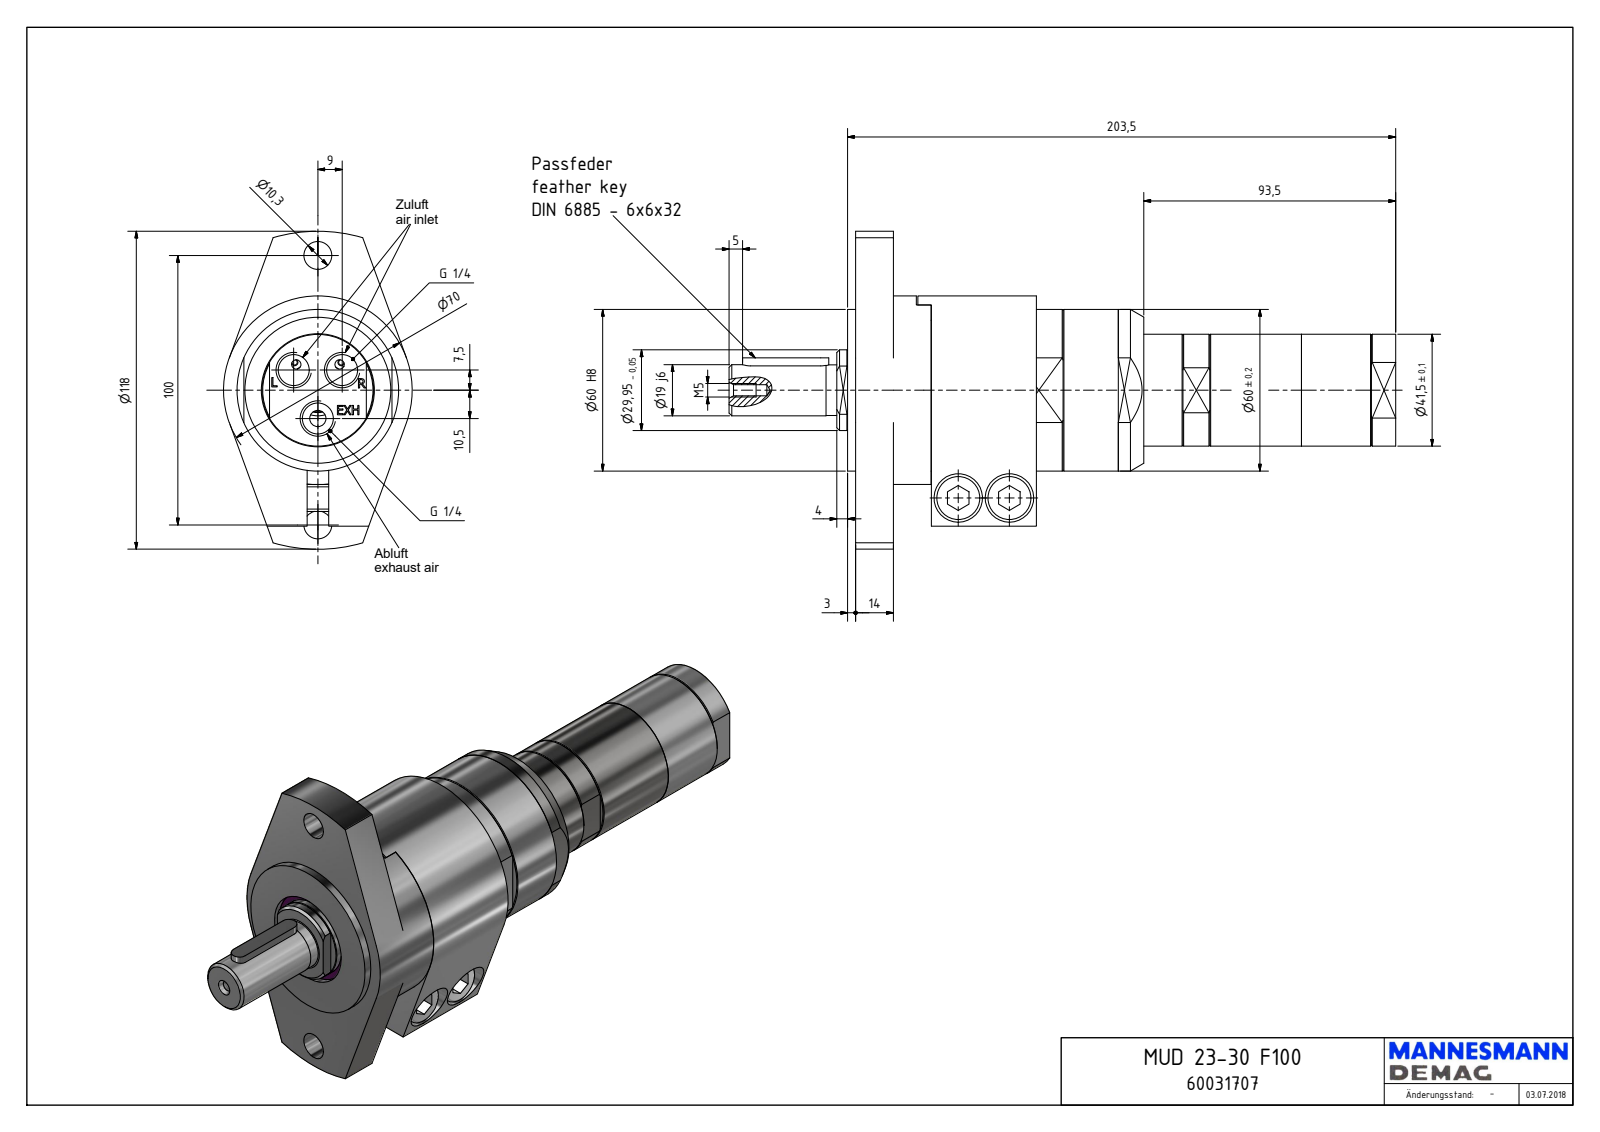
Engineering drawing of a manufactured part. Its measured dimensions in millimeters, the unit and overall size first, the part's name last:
Units: millimetres
Overall size (bounding box): 247.5 × 118 × 70
Round holes (diameter × count): ⌀11.45 ×3, ⌀8.38 ×2, ⌀10.3 ×2, ⌀10.5 ×2, ⌀18 ×2, ⌀4.13 ×1, ⌀35 ×1, ⌀42 ×1
Round bosses / shafts (diameter × count): ⌀16 ×2, ⌀10 ×2, ⌀70 ×1, ⌀63.41 ×1, ⌀60 ×1, ⌀55.18 ×1, ⌀41.5 ×1, ⌀29.95 ×1
Partial cylindrical surfaces — rounded edges, fillets, slot ends (radius × count): R3 ×2, R27.87 ×1, R59 ×1
Main face-to-face distances: 14, 17, 3, 70.1, 67.1, 53.1, 39, 70.01, 31.1, 28.1
Hole centre spacings: 11.72, 20.12, 43.44, 50, 58.2, 10.5, 18, 19
Volume: 568 298 mm³ · Surface area: 65 747 mm²
Bodies: 1 solid, 237 faces (146 planar, 50 cylindrical, 41 other)
Part name (STEP PRODUCT): MUD 23-30 F100_60031707
STEP written by: Autodesk Inventor 2018 (AUTOMOTIVE_DESIGN)
